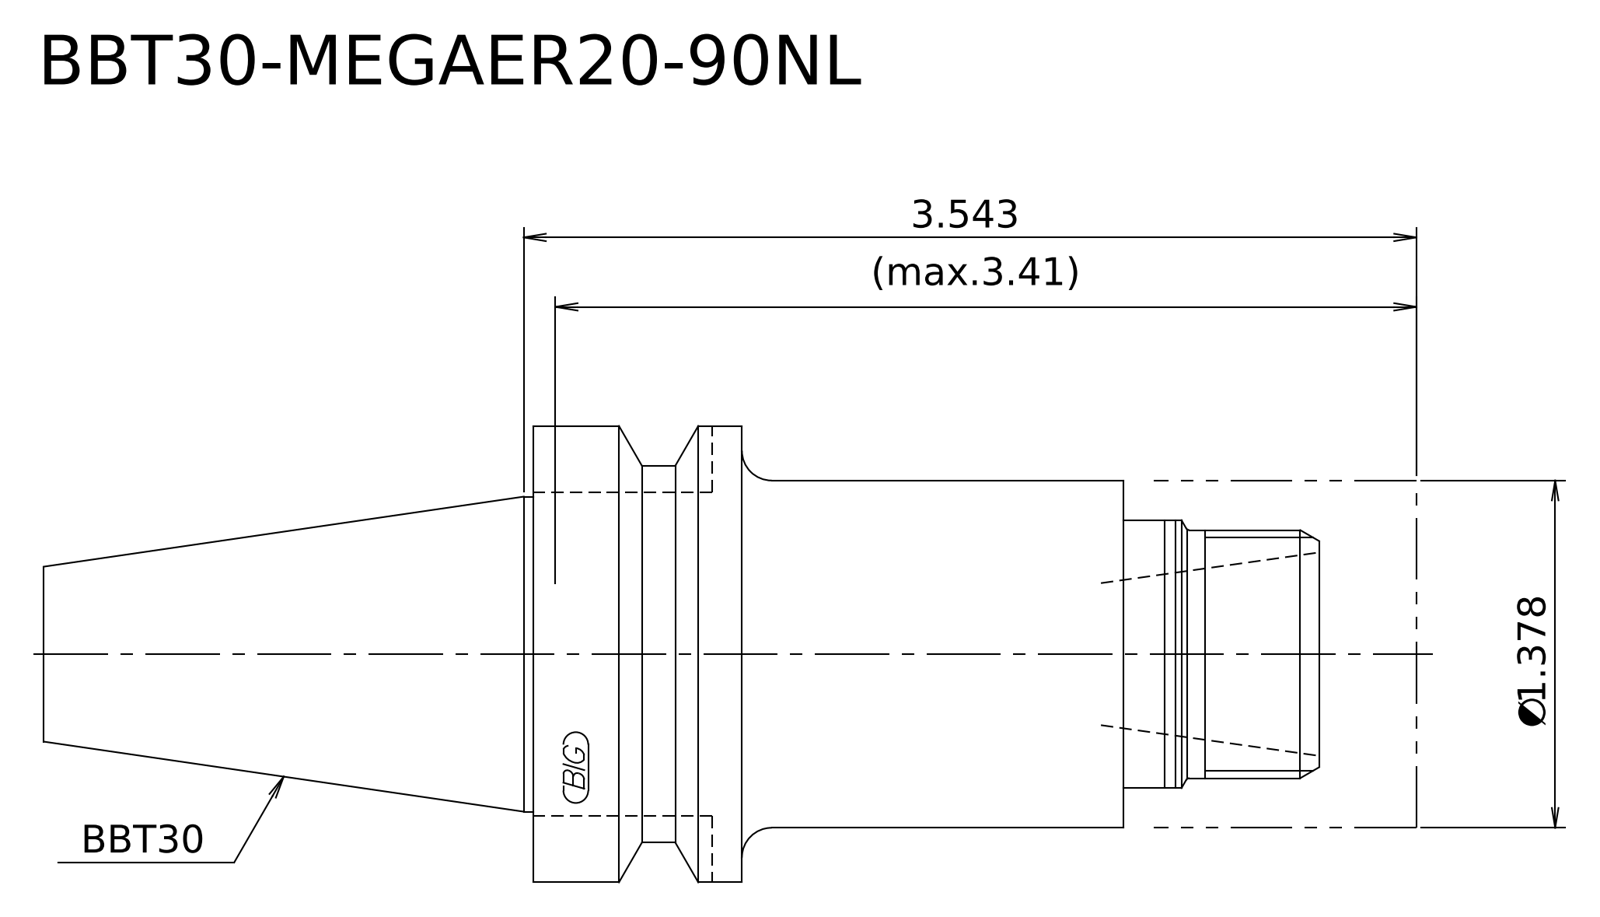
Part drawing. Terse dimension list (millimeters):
written by: Kubotek KeyCreator 2011 V10.0.2 (22737) (automotive_design)
unit: mm
bodies: 2 solids, 21 faces (7 planar, 8 cylindrical, 6 other)
size: 138.4 × 46 × 46
volume: 129 606 mm³; area: 20 545 mm²
bosses: 1× ⌀46, 1× ⌀38, 1× ⌀35, 1× ⌀31.75, 1× ⌀27, 1× ⌀25
face distances: 26.5, 89, 62.5, 9.8, 16.7, 79.2, 29.5, 19.7, 3, 59.5
